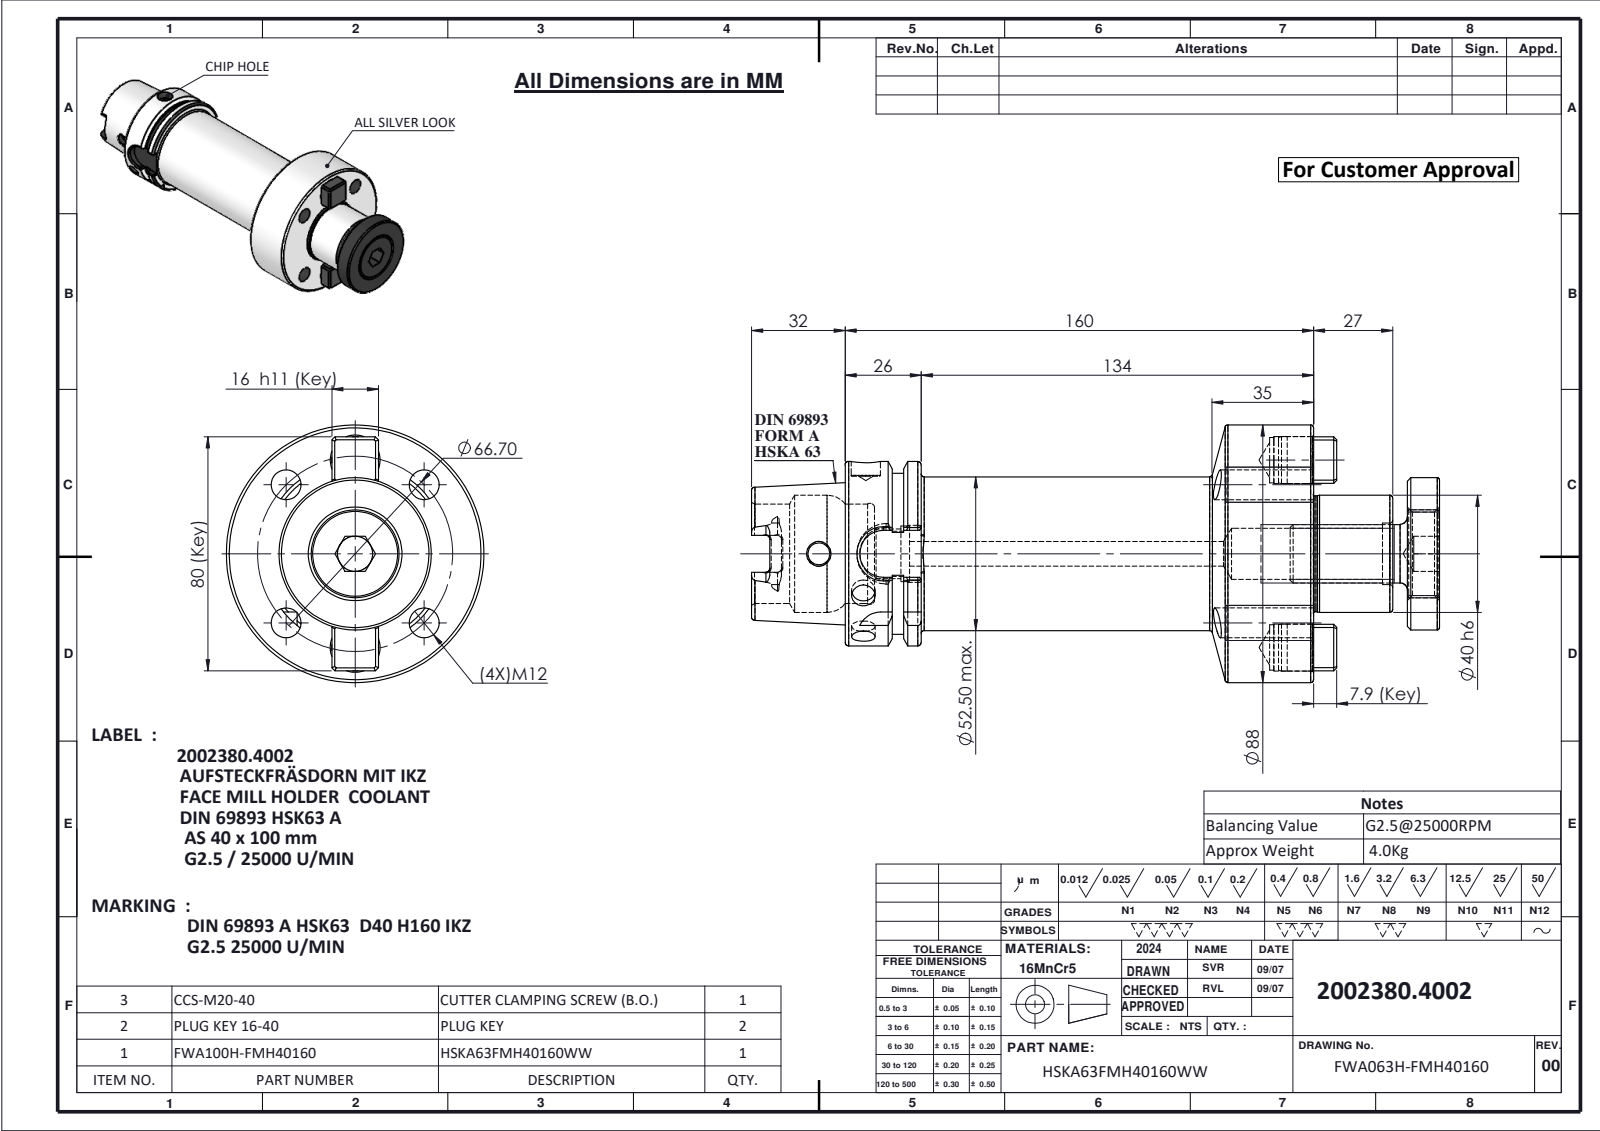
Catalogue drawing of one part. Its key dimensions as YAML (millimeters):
part_name: "CCS-M20-40-2; CCS-M20-40-1; FWA063H-FMH40160; HSKA100FMH40160WW (+2 more)"
step_written_by: "SolidWorks 2024 (CONFIG_CONTROL_DESIGN)"
units: millimeters
bodies: {solids: 5, faces: 339, planar: 109, cylindrical: 97, other: 133}
overall_size: [234.95, 88, 88]
volume: 537800
surface_area: 82518
round_holes:
  - {diameter: 10.2, count: 4}
  - {diameter: 8, count: 2}
  - {diameter: 15.5, count: 2}
  - {diameter: 16, count: 2}
  - {diameter: 7.5, count: 1}
  - {diameter: 8.4, count: 1}
  - {diameter: 10, count: 1}
  - {diameter: 17, count: 1}
  - {diameter: 17.5, count: 1}
  - {diameter: 19, count: 1}
  - {diameter: 21, count: 1}
  - {diameter: 28.5, count: 1}
round_bosses_or_shafts:
  - {diameter: 16.02, count: 2}
  - {diameter: 16.02, count: 2}
  - {diameter: 88, count: 1}
  - {diameter: 63, count: 1}
  - {diameter: 55, count: 1}
  - {diameter: 52.5, count: 1}
  - {diameter: 52, count: 1}
  - {diameter: 39.6, count: 1}
partial_cylinders:
  - {radius: 1.3, count: 6}
  - {radius: 2.88, count: 4}
  - {radius: 8, count: 2}
  - {radius: 10.5, count: 2}
  - {radius: 9, count: 1}
face_to_face_distances: [43, 32, 191.95, 11, 159.95, 202.95, 16, 12, 186.95, 27]
hole_center_spacings: [33.35, 60.38, 25.04, 25.05, 32, 47.16, 47.17, 66.7]
